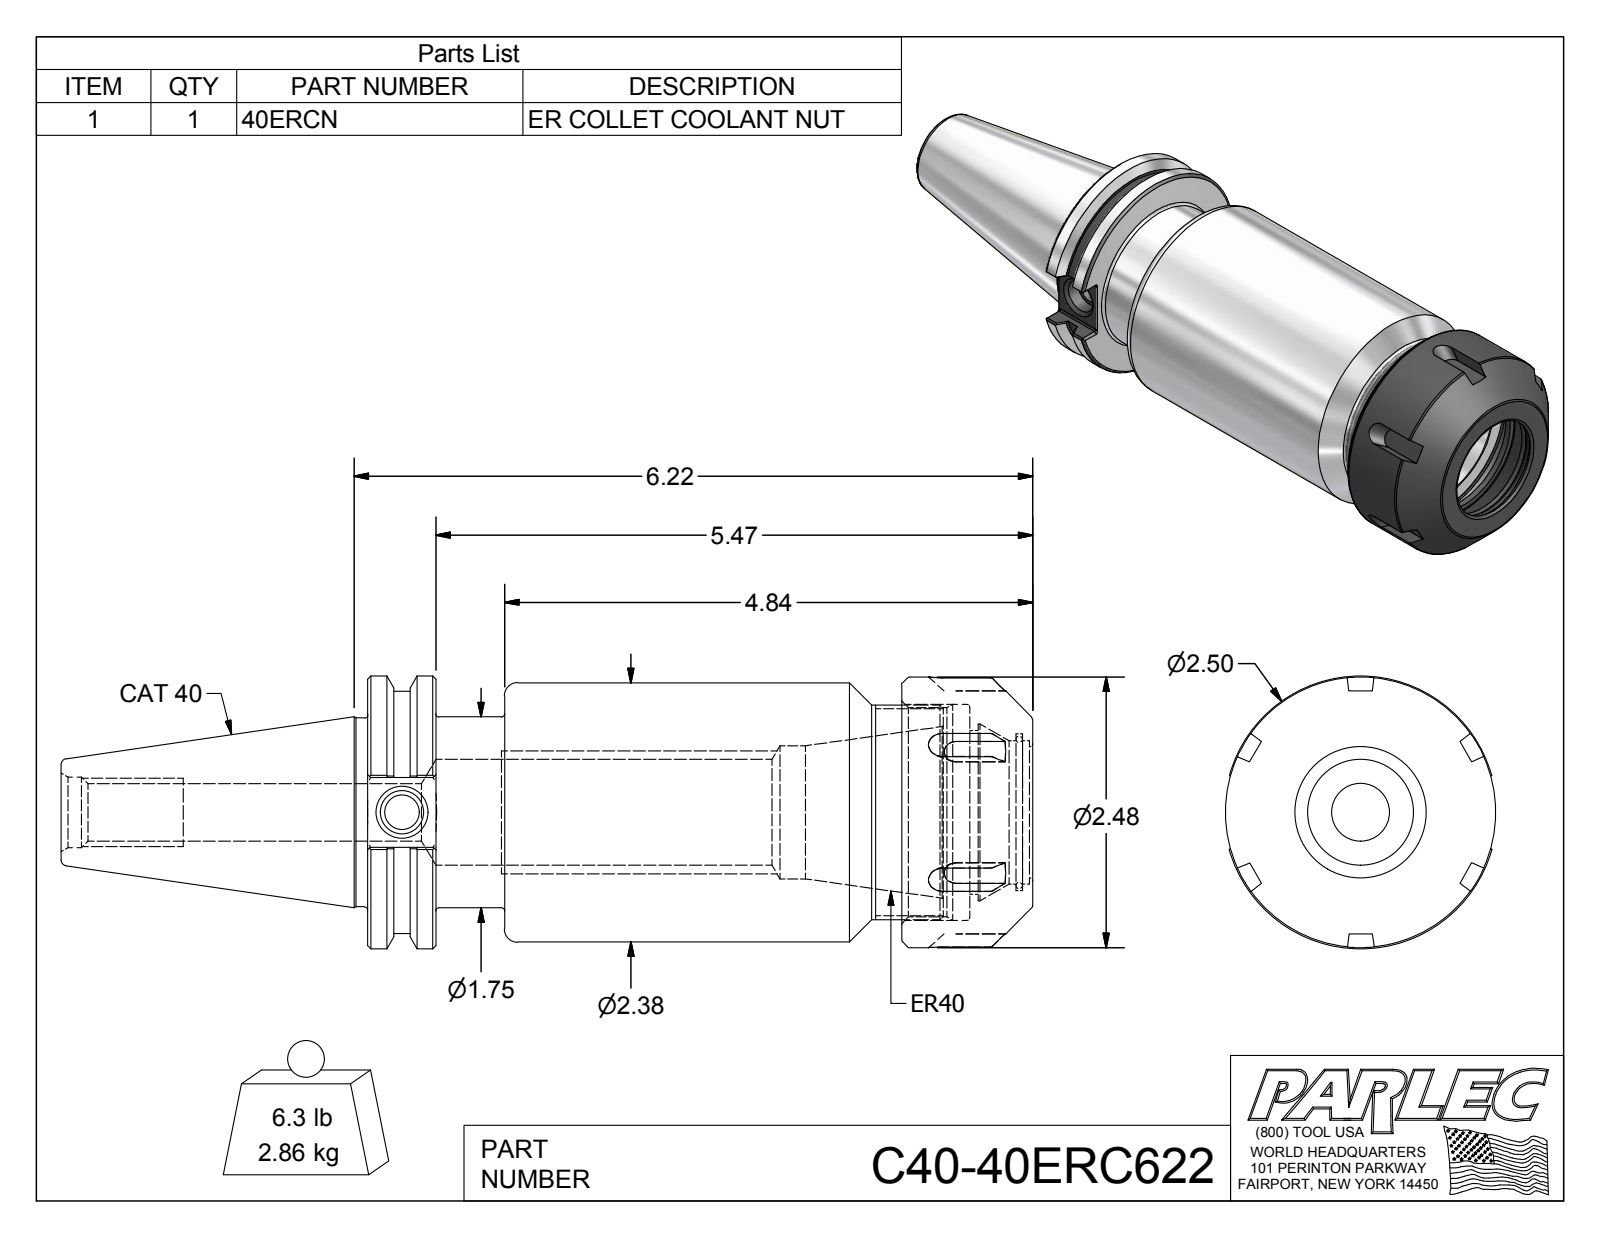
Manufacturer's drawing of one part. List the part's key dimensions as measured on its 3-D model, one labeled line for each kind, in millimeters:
Part name (STEP PRODUCT): C40-40ERC622; C40-40ER6-1; 40ERCN
STEP written by: Autodesk Inventor 2012 (AUTOMOTIVE_DESIGN)
Units: millimetres
Bodies: 2 solids, 151 faces (58 planar, 36 cylindrical, 57 other)
Overall size (bounding box): 226.2 × 63.5 × 63
Volume: 364 000 mm³ · Surface area: 67 230 mm²
Round holes (diameter × count): ⌀8 ×1, ⌀10.1 ×1, ⌀13.4 ×1, ⌀16.5 ×1, ⌀24.6 ×1, ⌀31 ×1, ⌀33.4 ×1, ⌀36.5 ×1, ⌀38.1 ×1, ⌀41.1 ×1, ⌀48.7 ×1, ⌀50.3 ×1
Round bosses / shafts (diameter × count): ⌀63.5 ×1, ⌀63 ×1, ⌀60.3 ×1, ⌀56.4 ×1, ⌀50 ×1, ⌀44.5 ×1, ⌀43.9 ×1
Partial cylindrical surfaces — rounded edges, fillets, slot ends (radius × count): R0.5 ×12
Main face-to-face distances: 15.9, 124.3, 140.2, 154.8, 138.9, 14.6, 31.9, 16, 108.3, 122.9
